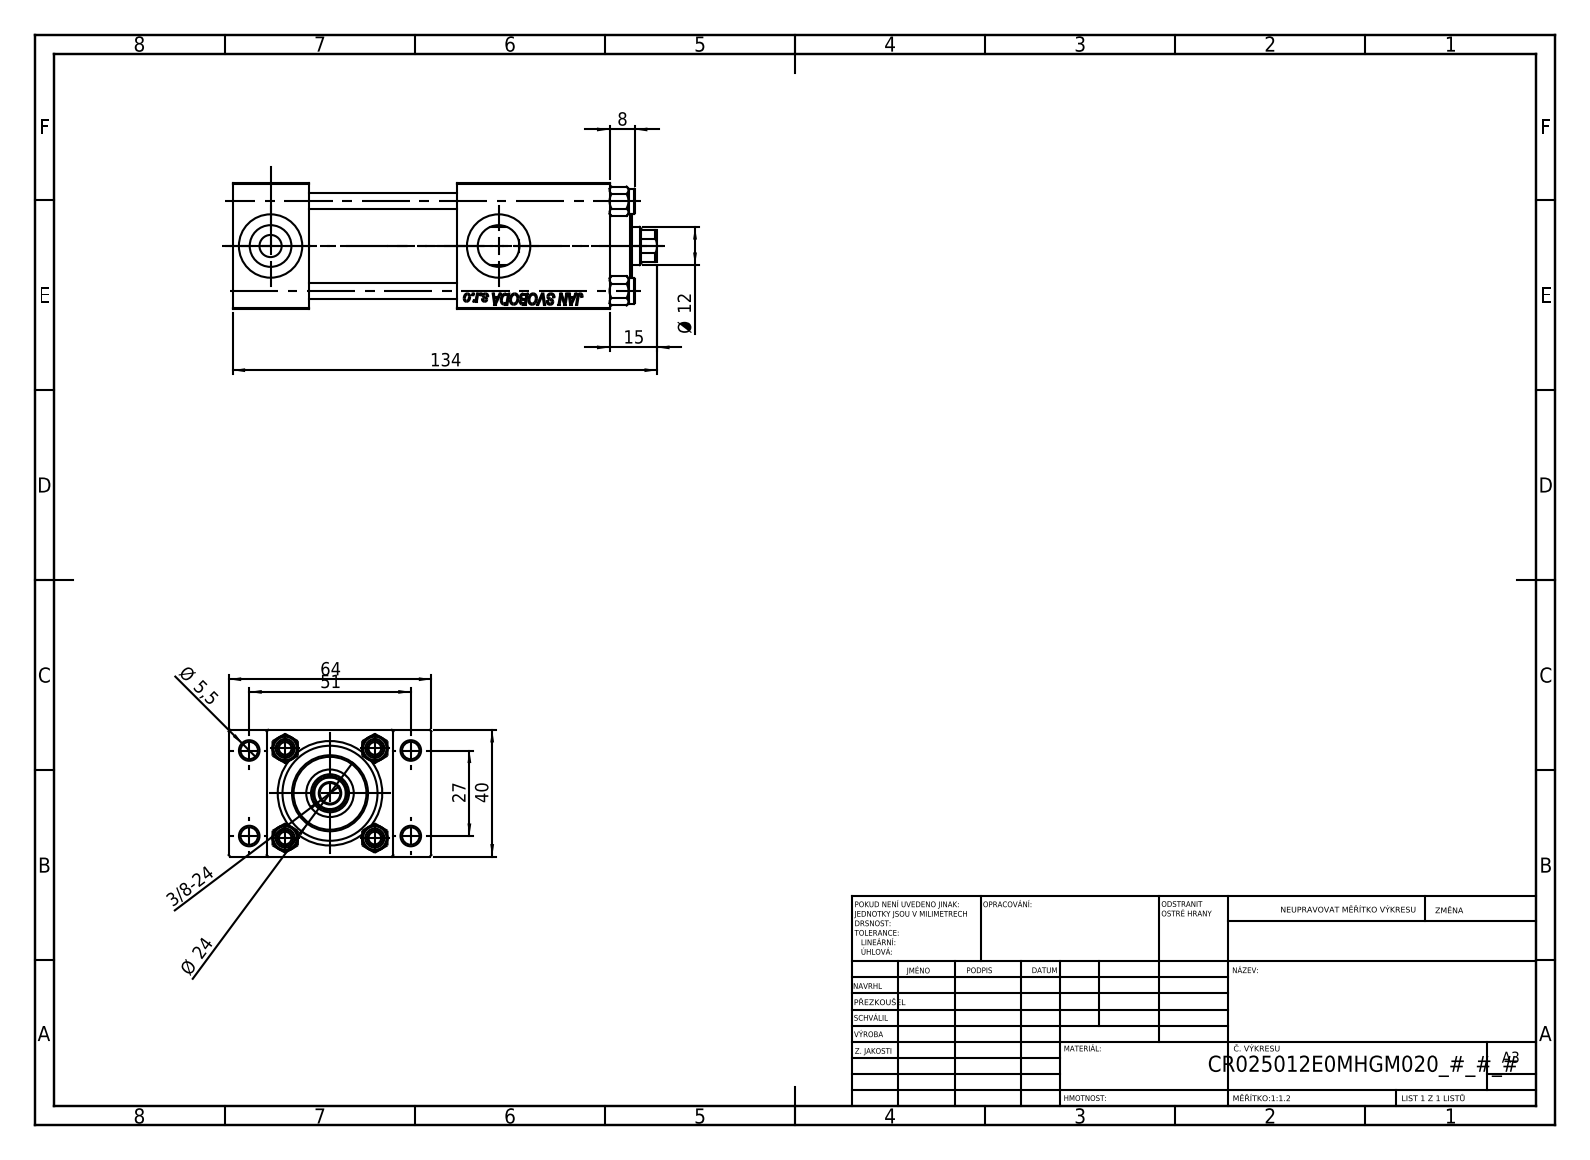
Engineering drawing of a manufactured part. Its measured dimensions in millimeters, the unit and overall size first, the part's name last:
Units: millimetres
Overall size (bounding box): 134 × 64 × 40
Round holes (diameter × count): ⌀5 ×4, ⌀5.5 ×4, ⌀20 ×3, ⌀7 ×2, ⌀13.16 ×2, ⌀6.5 ×1, ⌀12 ×1, ⌀15 ×1, ⌀25 ×1, ⌀30 ×1
Round bosses / shafts (diameter × count): ⌀8 ×4, ⌀31 ×1, ⌀24 ×1
Partial cylindrical surfaces — rounded edges, fillets, slot ends (radius × count): R5.5 ×1
Main face-to-face distances: 40, 24, 12, 52, 119, 95, 90.3, 66.3, 28.7, 47
Hole centre spacings: 11.37, 20.01, 28.3, 28.85, 29.89, 39.66, 48.34, 27
Volume: 163 534 mm³ · Surface area: 62 368 mm²
Bodies: 11 solids, 1135 faces (497 planar, 86 cylindrical, 552 other)
Part name (STEP PRODUCT): V215_VC_A; V215CR_VCP_E; V215CR_TYCINKA_E; V215CR_E_Body (+1 more)
STEP written by: SolidWorks 2019 (CONFIG_CONTROL_DESIGN)
